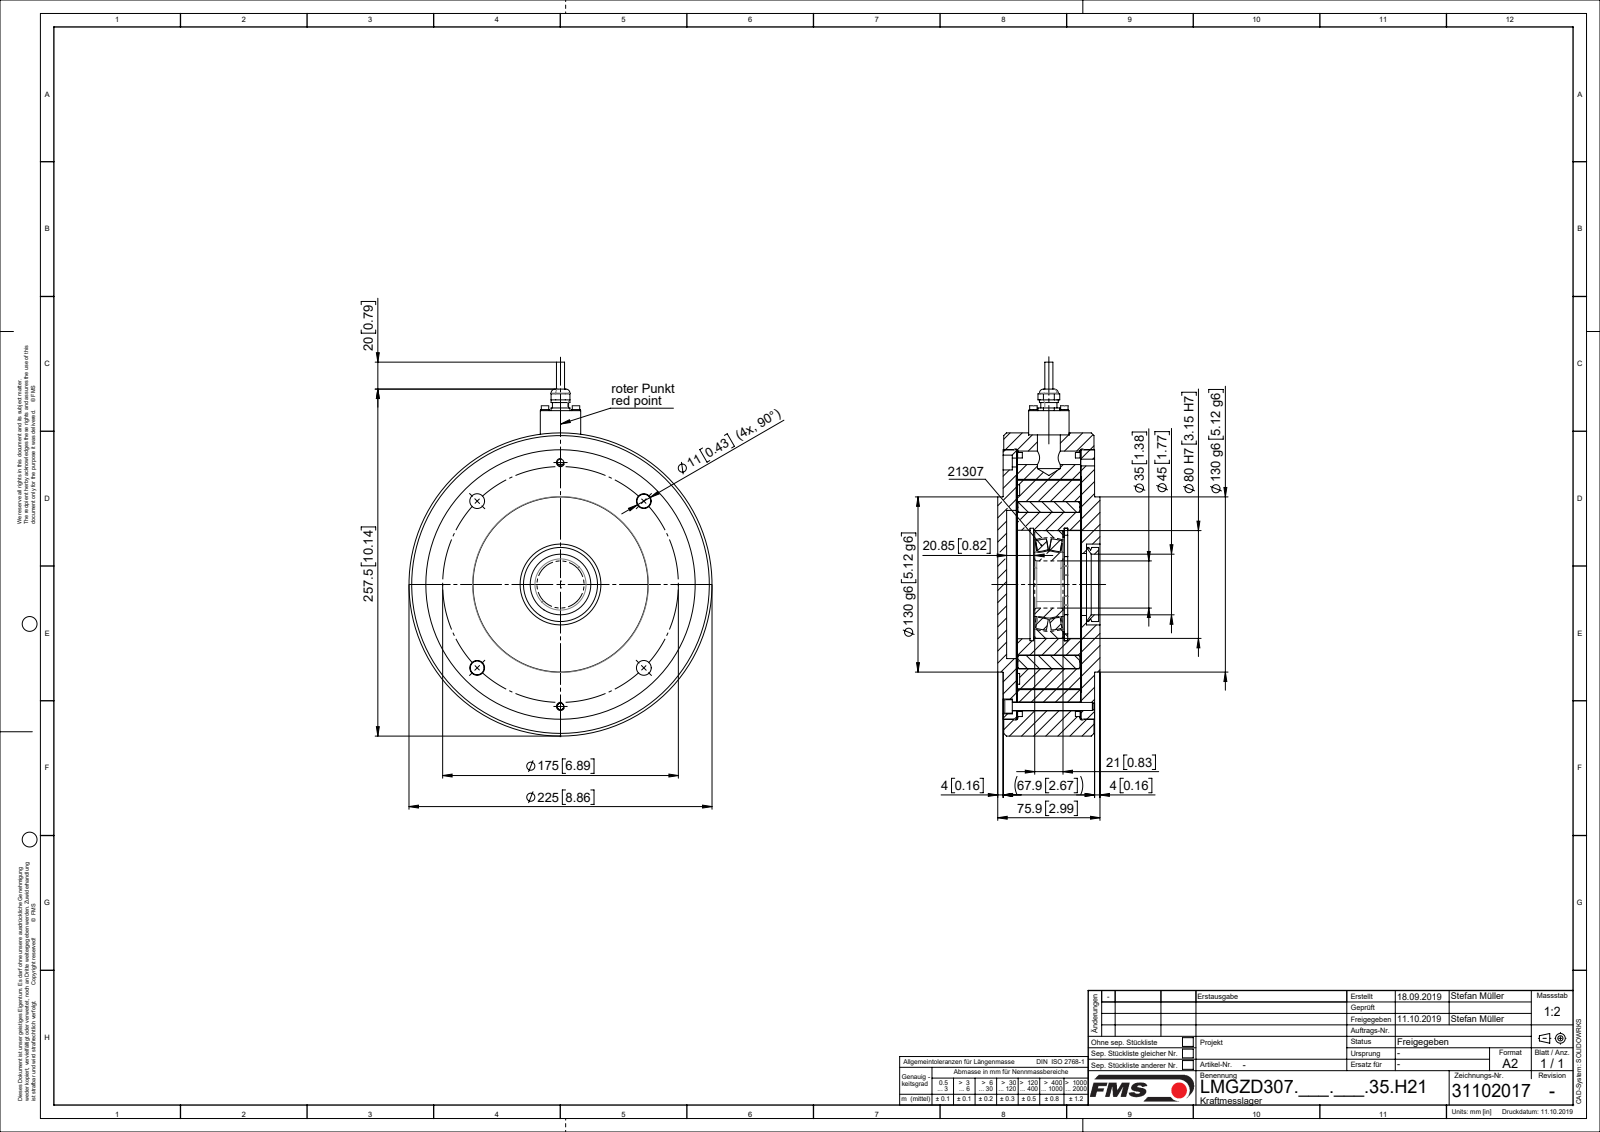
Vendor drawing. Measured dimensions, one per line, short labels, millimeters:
name: 43404.02_01; 49651-04_stp_01; Zyl-Schr DIN912_M6x60; 48072_01 (+8 more)
written by: SolidWorks 2018 (CONFIG_CONTROL_DESIGN)
unit: mm
bodies: 52 solids, 736 faces (218 planar, 263 cylindrical, 255 other)
size: 277.5 × 225 × 75.9
volume: 2 389 000 mm³; area: 444 973 mm²
holes: 6× ⌀11, 4× ⌀2.5, 4× ⌀3.1, 4× ⌀3.4, 2× ⌀3, 2× ⌀5, 2× ⌀6.6, 2× ⌀10, 2× ⌀10.2, 1× ⌀6, 1× ⌀8, 1× ⌀11.5
bosses: 4× ⌀6.2, 4× ⌀5.5, 4× ⌀3, 1× ⌀225, 1× ⌀199, 1× ⌀188, 1× ⌀140, 1× ⌀132
rounds: 4× R0.1, 4× R11, 2× R4.91, 1× R33.25, 1× R79, 1× R82, 1× R86
face distances: 47.25, 10.2, 10.45, 57.45, 57.7, 0.5, 0.75, 47.75, 48, 9.7
hole spacings: 16.26, 23, 62.02, 68.17, 87.5, 123.74, 134.45, 164.45
